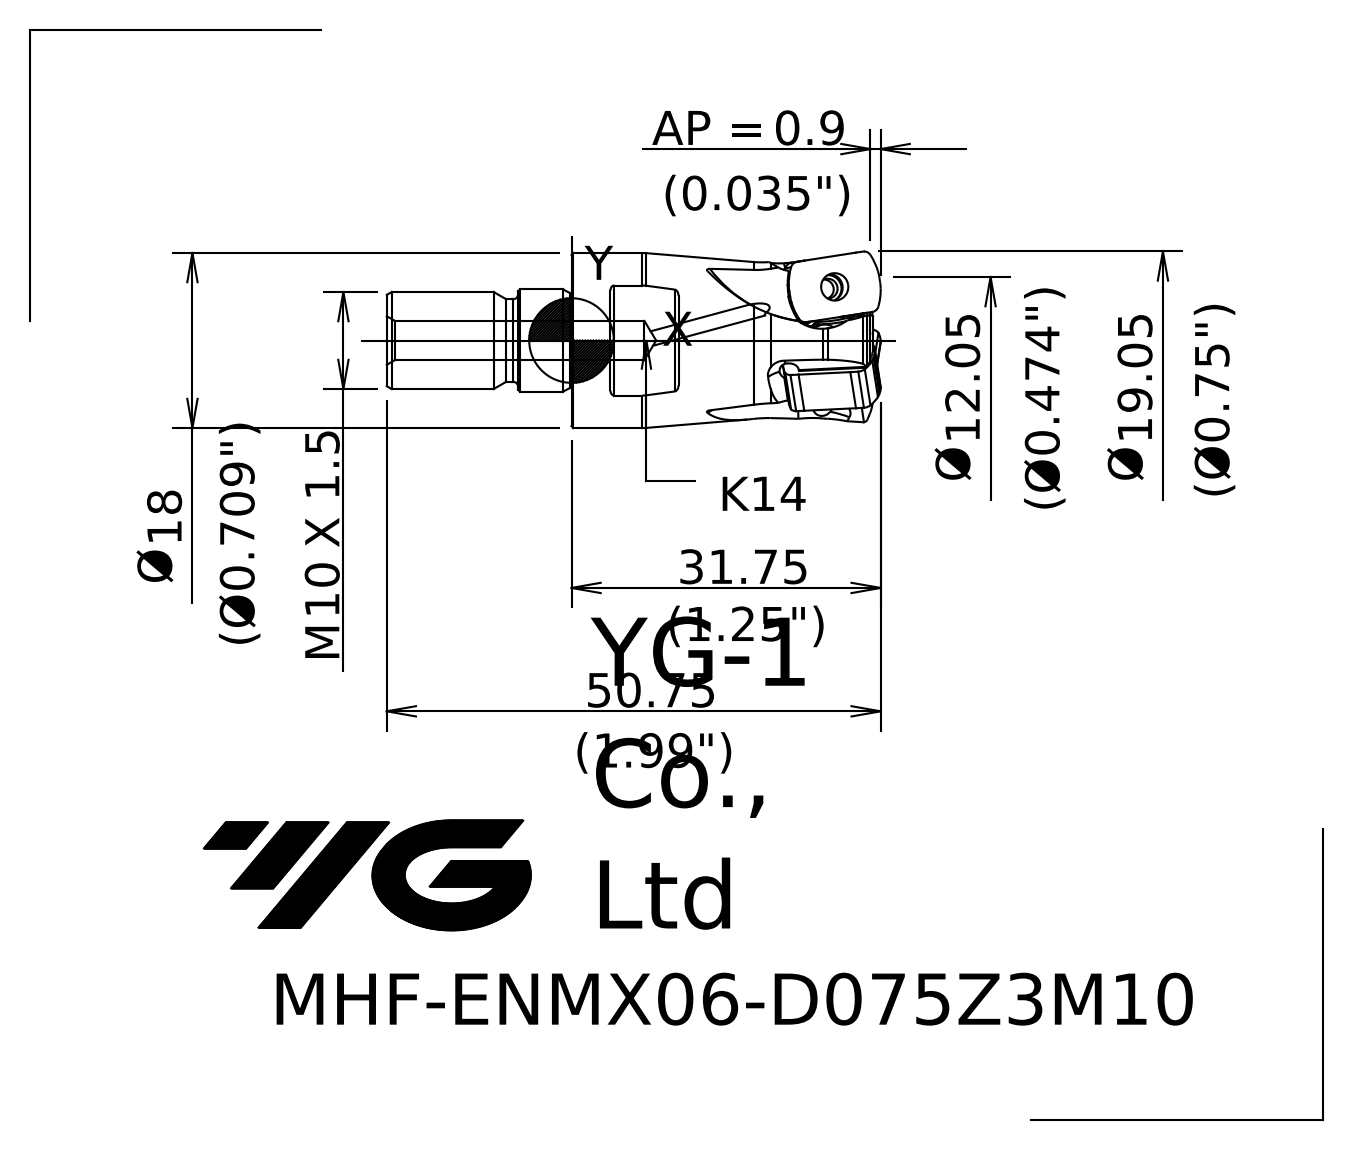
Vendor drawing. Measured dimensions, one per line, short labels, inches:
name: 12011488FE3F3cxe
written by: SIEMENS PLM Software NX 10.0 (AP203_CONFIGURATION_CONTROLLED_3D_DESIGN_OF_MECHANICAL_PARTS_AND_ASSEMBLIES_MIM_LF)
unit: in
bodies: 1 solid, 74 faces (12 planar, 10 cylindrical, 52 other)
size: 1.998 × 0.751 × 0.751
volume: 0.478 in³; area: 5.03 in²
holes: 1× ⌀0.157
bosses: 1× ⌀0.709, 1× ⌀0.413, 1× ⌀0.393, 1× ⌀0.346, 1× ⌀0.32
rounds: 4× R0.016
face distances: 0.551, 0.748, 0.157, 0.906, 0.276, 0.433, 1.181, 0.77, 1.045, 1.203
